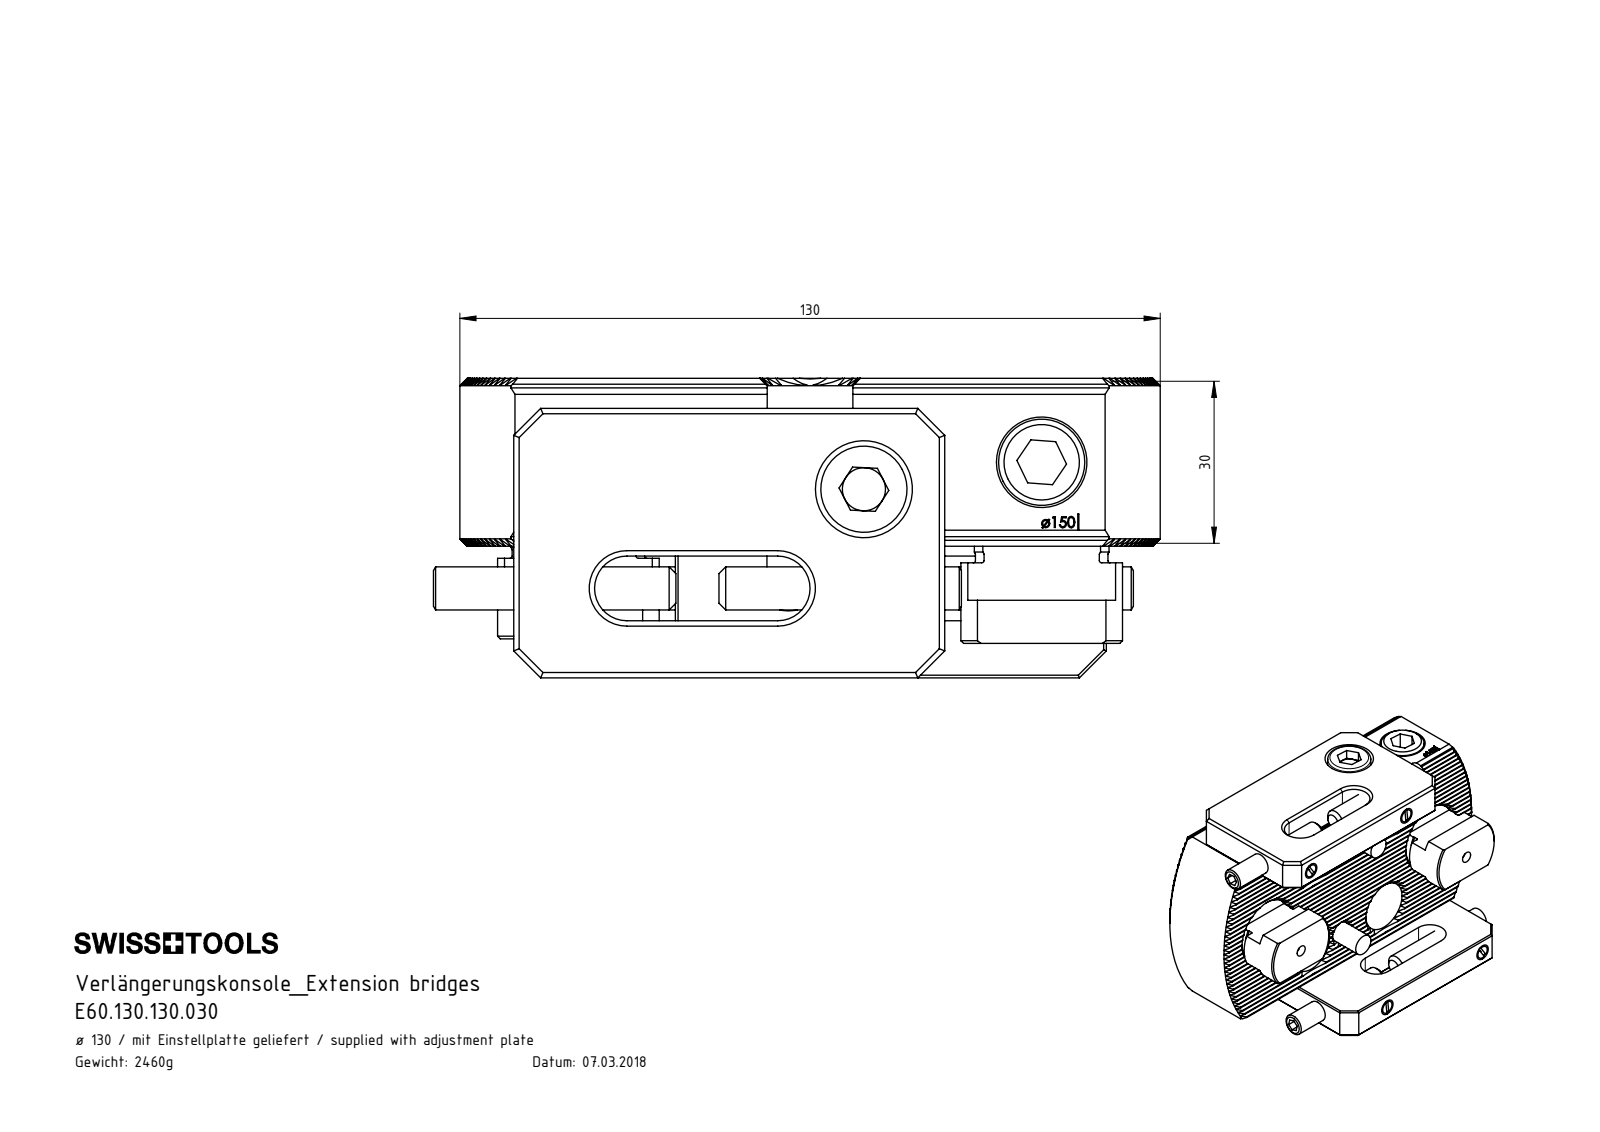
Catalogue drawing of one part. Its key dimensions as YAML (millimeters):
part_name: "VK1-ER3.001.028_A_PreviewCfg; VK1-ER7.001.012_mit kurzer Schraube; ISO 4766 - M6x12_ISO 4766 - M6 x 10; DIN 6912 - M10 x 12 (+8 more)"
step_written_by: "SolidWorks 2017 (CONFIG_CONTROL_DESIGN)"
units: millimeters
bodies: {solids: 27, faces: 1743, planar: 968, cylindrical: 467, other: 308}
overall_size: [130, 95, 55.58]
volume: 319917
surface_area: 101240
round_holes:
  - {diameter: 5, count: 4}
  - {diameter: 6, count: 4}
  - {diameter: 6.8, count: 4}
  - {diameter: 13, count: 4}
  - {diameter: 19, count: 4}
  - {diameter: 2, count: 2}
  - {diameter: 8, count: 2}
  - {diameter: 8.5, count: 2}
  - {diameter: 10.5, count: 2}
  - {diameter: 11, count: 2}
  - {diameter: 14, count: 2}
  - {diameter: 18, count: 2}
round_bosses_or_shafts:
  - {diameter: 16, count: 4}
  - {diameter: 6, count: 4}
  - {diameter: 10, count: 2}
  - {diameter: 8, count: 2}
partial_cylinders:
  - {radius: 0.14, count: 66}
  - {radius: 2, count: 8}
  - {radius: 6, count: 4}
  - {radius: 12.3, count: 2}
  - {radius: 15, count: 2}
  - {radius: 7.95, count: 1}
  - {radius: 65, count: 1}
face_to_face_distances: [12, 82, 70, 0.5, 82.5, 11.5, 1.73, 70.5, 94, 71]
hole_center_spacings: [31.24, 65.15, 86, 2.05, 6.67, 7.9, 15, 17]
